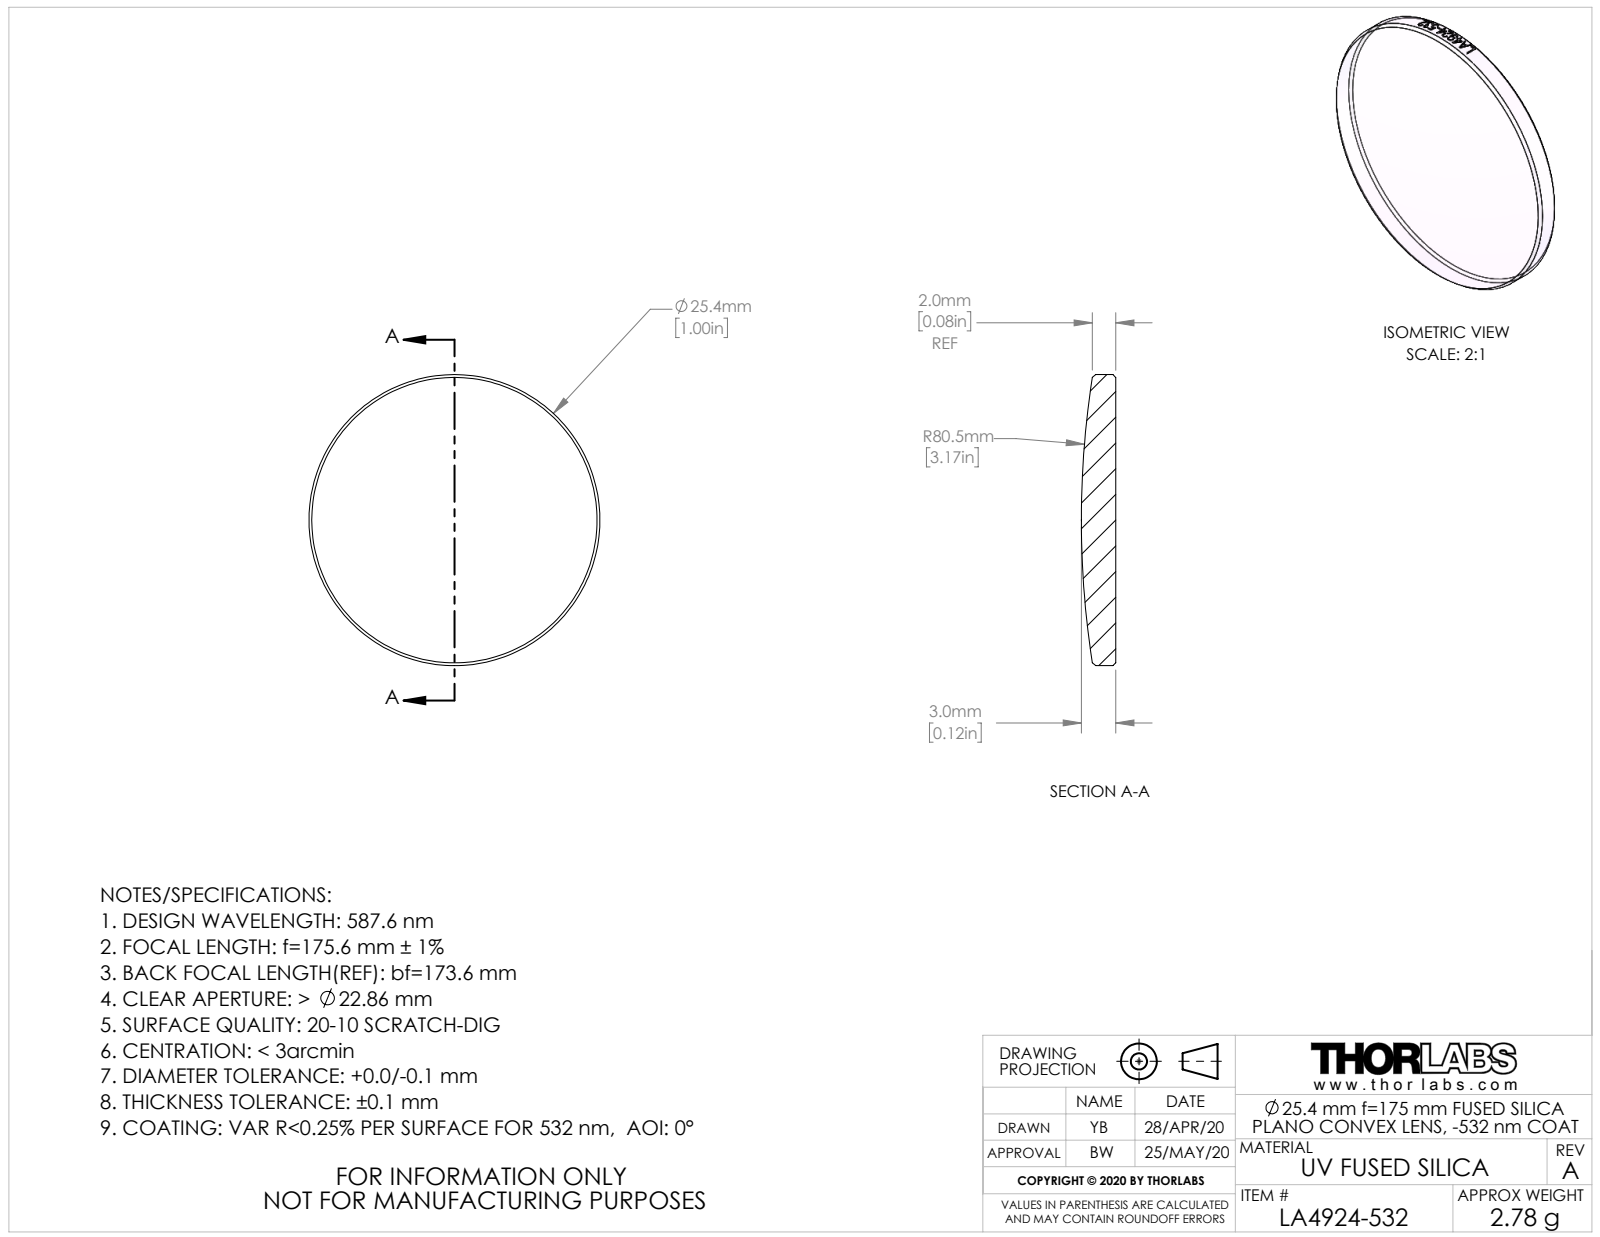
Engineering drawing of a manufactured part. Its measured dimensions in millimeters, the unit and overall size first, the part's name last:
Units: millimetres
Overall size (bounding box): 25.4 × 25.4 × 3
Round bosses / shafts (diameter × count): ⌀25.4 ×1
Volume: 1 263 mm³ · Surface area: 1 155 mm²
Bodies: 1 solid, 28 faces (1 planar, 21 cylindrical, 6 other)
Part name (STEP PRODUCT): CTN015720-E0W
STEP written by: SolidWorks 2018 (AUTOMOTIVE_DESIGN)
